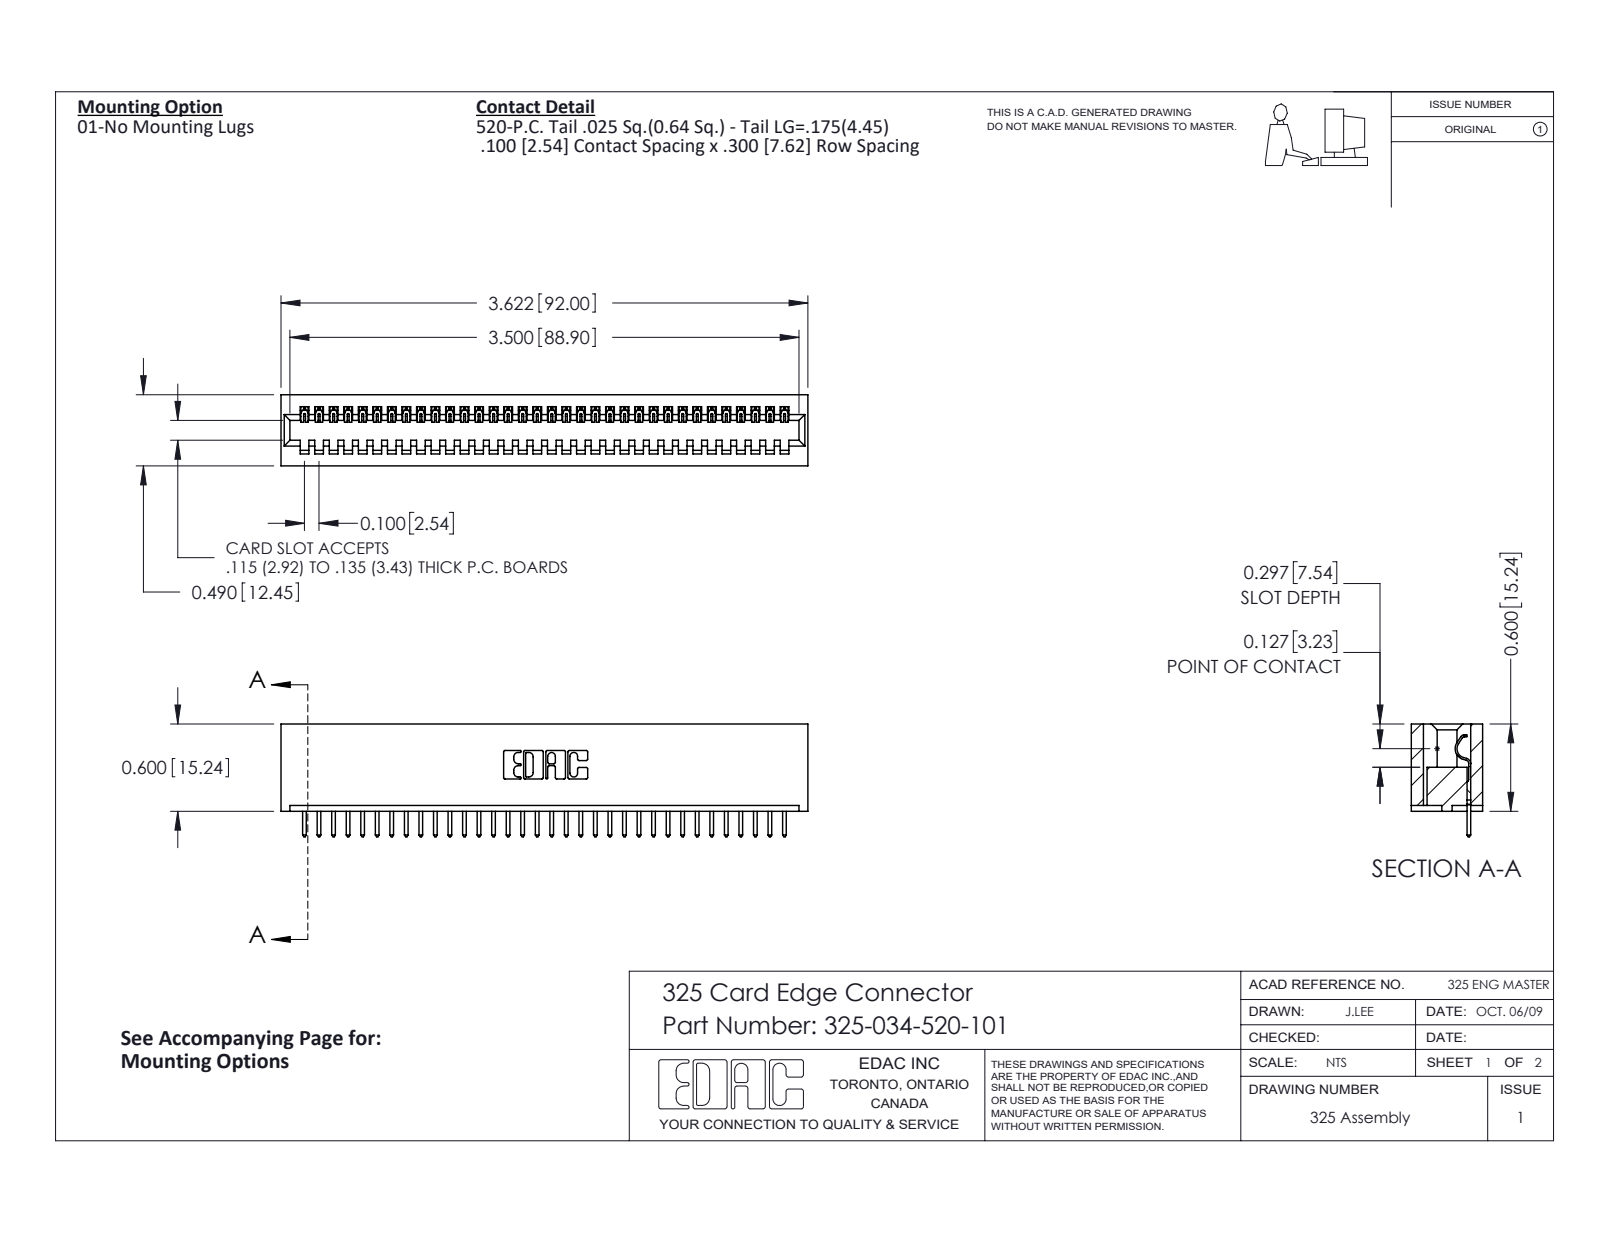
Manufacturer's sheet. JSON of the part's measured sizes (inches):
{"part_name": "325-034-520-101; 325-292-001_325-293-120; 325 Part_Lugless", "step_written_by": "SolidWorks 2016 (CONFIG_CONTROL_DESIGN)", "units": "inches", "bodies": {"solids": 35, "faces": 2078, "planar": 1494, "cylindrical": 584, "other": 0}, "overall_size": [3.622, 0.775, 0.49], "volume_in3": 0.738, "surface_area_in2": 20.49, "partial_cylinders_radius": [[0.006, 68], [0.01, 68], [0.01, 22], [0.007, 6], [0.031, 6], [0.026, 3], [0.014, 1], [0.022, 1]], "face_to_face_distances": [0.083, 0.407, 0.49, 0.3, 0.107, 0.383, 0.025, 0.325, 0.1, 0.56]}
